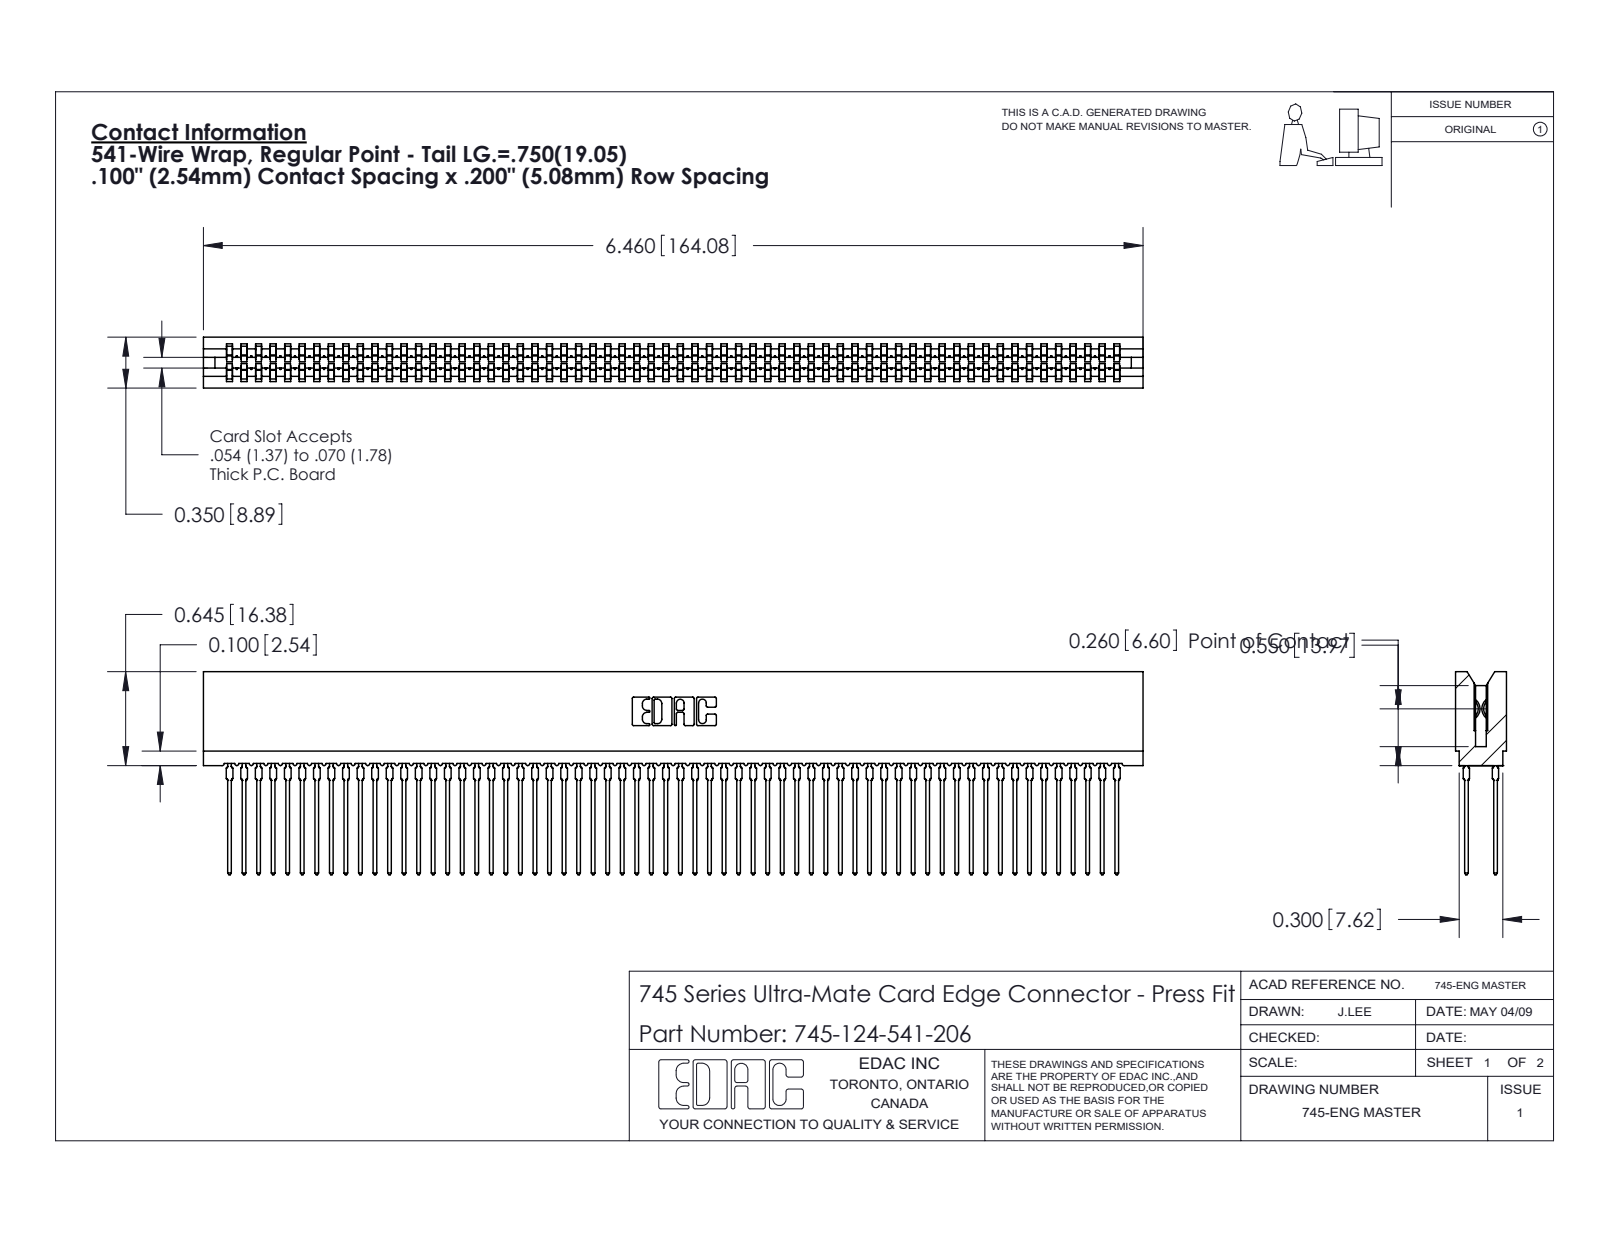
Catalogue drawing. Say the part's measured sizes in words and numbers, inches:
The part is named "745-292-001_541; 745 Part_Insulator Option - 06; 745-124-541-206". Its 3-D file was written by "SolidWorks 2020 (CONFIG_CONTROL_DESIGN)". It is 125 solids with 11194 faces: 5760 planar, 2210 cylindrical and 3224 other. Overall it measures 6.46 by 1.396 by 0.35 inches. Its volume is 0.93 cubic inches and its surface area 52.6 square inches. Partial cylindrical surfaces (rounded edges, fillets, slot ends): 248 of radius 0.021, 124 of radius 0.015, 22 of radius 0.01, 8 of radius 0.005, 8 of radius 0.011, 6 of radius 0.007, 6 of radius 0.031, 3 of radius 0.026. The main face-to-face distances are 0.063, 0.287, 0.2, 0.35, 0.087, 0.263, 0.025, 0.045, 0.305, 0.018.
